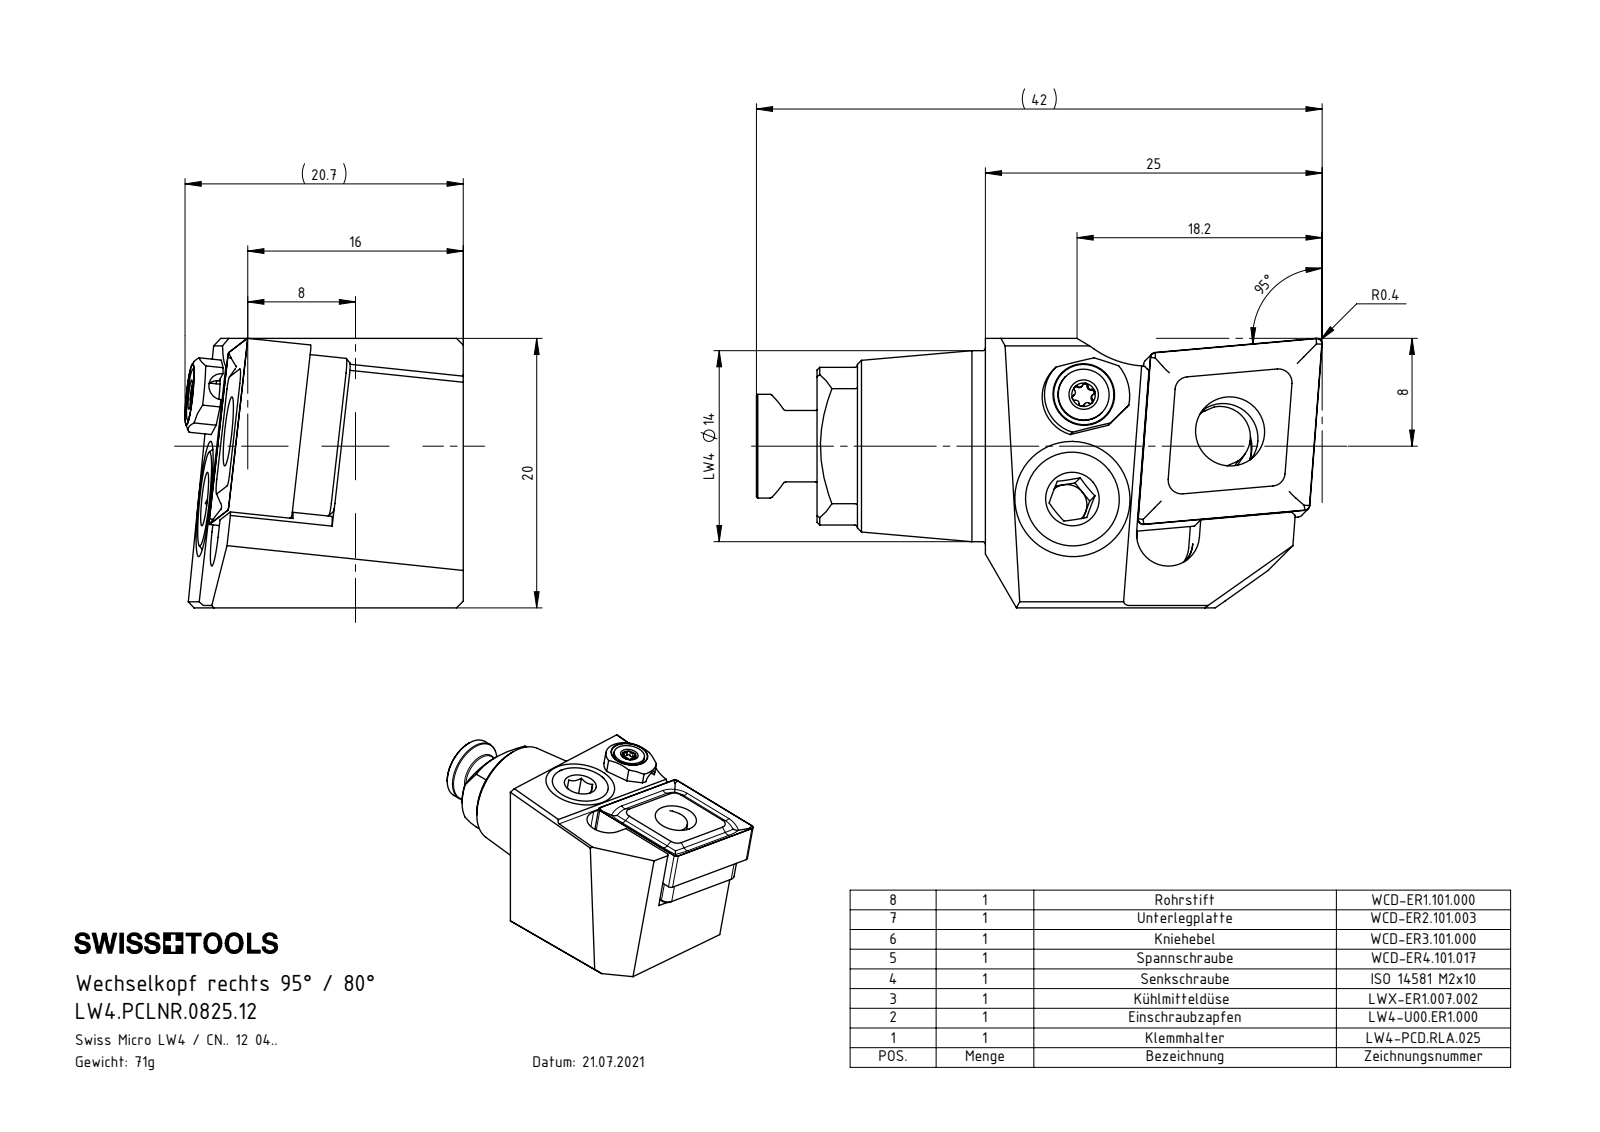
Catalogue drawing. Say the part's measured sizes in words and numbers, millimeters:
The part is named "WCD-ER2.101.003_A; WCD-ER4.101.017_A; LW4.PCLNR.0825.12; CNMG120404 (+4 more)". Its 3-D file was written by "SolidWorks 2022 (CONFIG_CONTROL_DESIGN)". It is 7 solids with 281 faces: 101 planar, 84 cylindrical and 96 other. Overall it measures 37.5 by 20.55 by 20 millimeters. Its volume is 7 836 cubic millimeters and its surface area 5 782 square millimeters. Round holes: 2 of diameter 3, 1 of diameter 1.6, 1 of diameter 2, 1 of diameter 5.16, 1 of diameter 5.5, 1 of diameter 6.55, 1 of diameter 7, 1 of diameter 8.4. Round bosses or shafts: 1 of diameter 14.17, 1 of diameter 8, 1 of diameter 7.9, 1 of diameter 6.4, 1 of diameter 4.5, 1 of diameter 3.8, 1 of diameter 3.55, 1 of diameter 2. Partial cylindrical surfaces (rounded edges, fillets, slot ends): 8 of radius 0.2, 6 of radius 0.24, 4 of radius 0.4, 4 of radius 1, 2 of radius 2.5, 1 of radius 0.5, 1 of radius 2.1, 1 of radius 2.2. The main face-to-face distances are 11.7, 4.76, 3.18, 7.94, 1, 12.7, 12.2, 11.2, 0.5, 5.6. The hole center spacings are 7.62, 11.39, 11.43, 12.86, 12.93.
